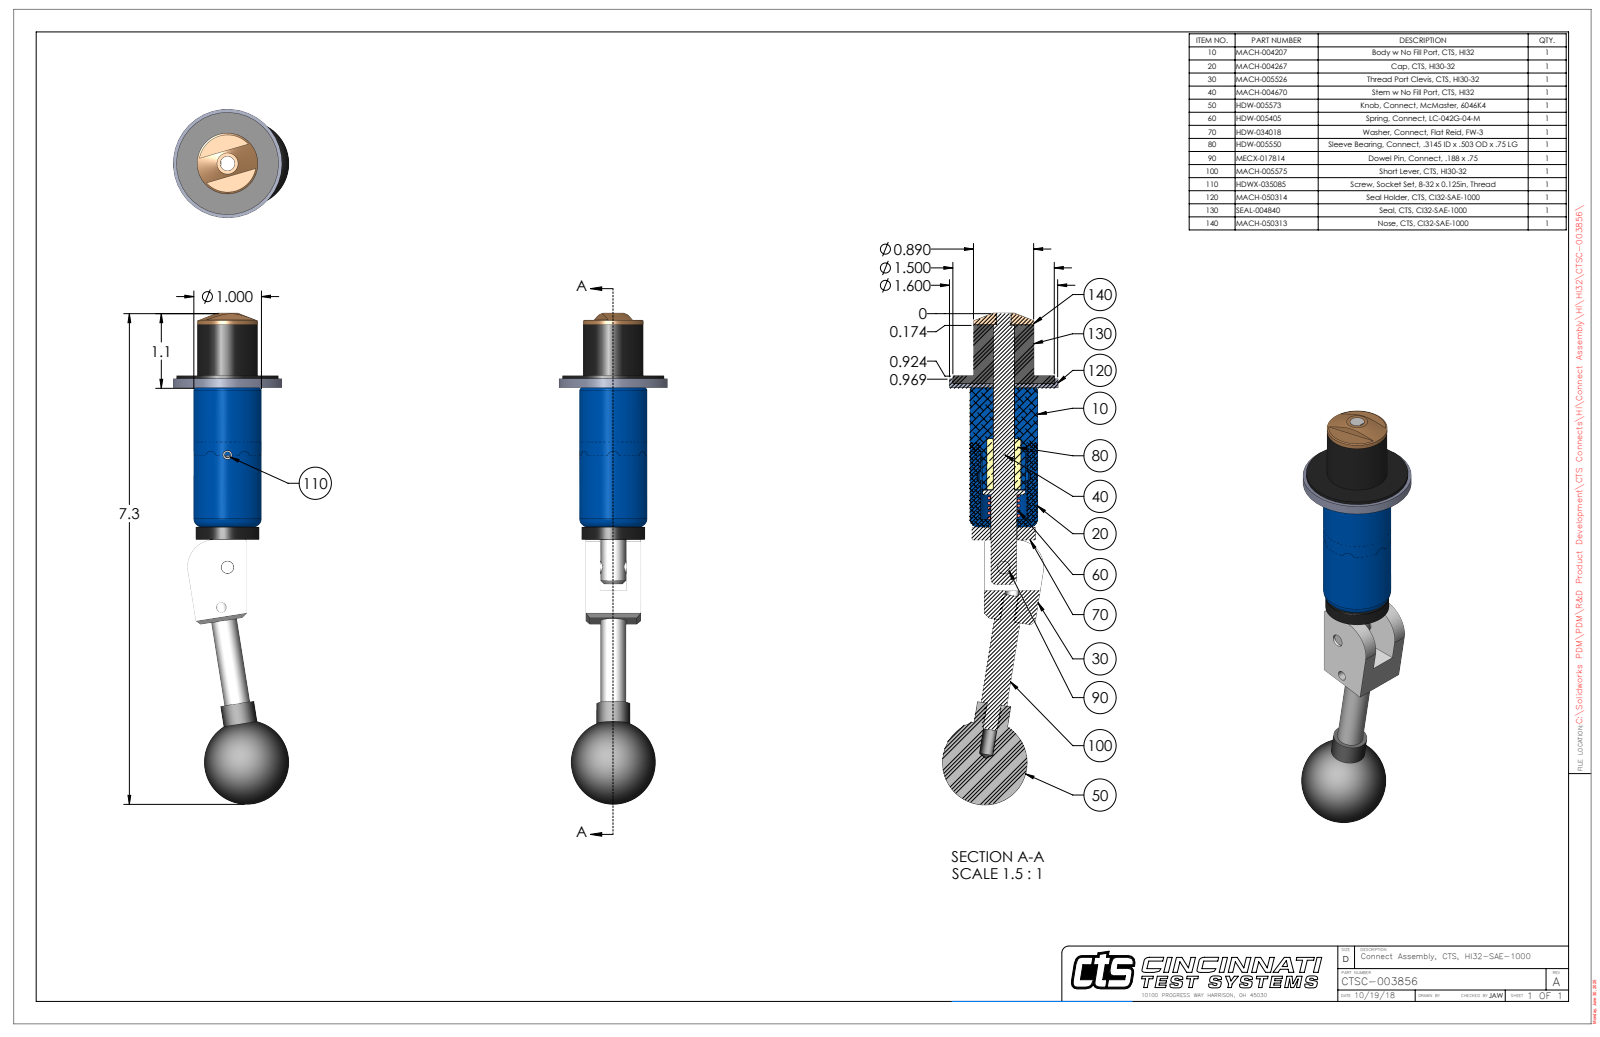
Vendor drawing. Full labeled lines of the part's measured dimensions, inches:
Part name (STEP PRODUCT): CTSC-003856
STEP written by: SolidWorks 2023 (AUTOMOTIVE_DESIGN)
Units: inches
Bodies: 9 solids, 196 faces (67 planar, 76 cylindrical, 53 other)
Overall size (bounding box): 7.256 × 1.705 × 1.6
Volume: 4.421 in³ · Surface area: 40.55 in²
Round holes (diameter × count): ⌀0.201 ×2, ⌀0.15 ×1, ⌀0.189 ×1, ⌀0.213 ×1, ⌀0.31 ×1, ⌀0.314 ×1, ⌀0.316 ×1, ⌀0.385 ×1, ⌀0.392 ×1, ⌀1.5 ×1
Round bosses / shafts (diameter × count): ⌀0.25 ×2, ⌀0.201 ×2, ⌀1.6 ×1, ⌀1 ×1, ⌀0.936 ×1, ⌀0.89 ×1, ⌀0.5 ×1, ⌀0.38 ×1
Partial cylindrical surfaces — rounded edges, fillets, slot ends (radius × count): R0.029 ×2, R0.068 ×1, R0.4 ×1, R0.459 ×1
Main face-to-face distances: 0.06, 0.75, 0.87, 0.93, 0.21, 0.602, 0.12, 0.18, 3.172, 2.985
Hole centre spacings: 0.599
